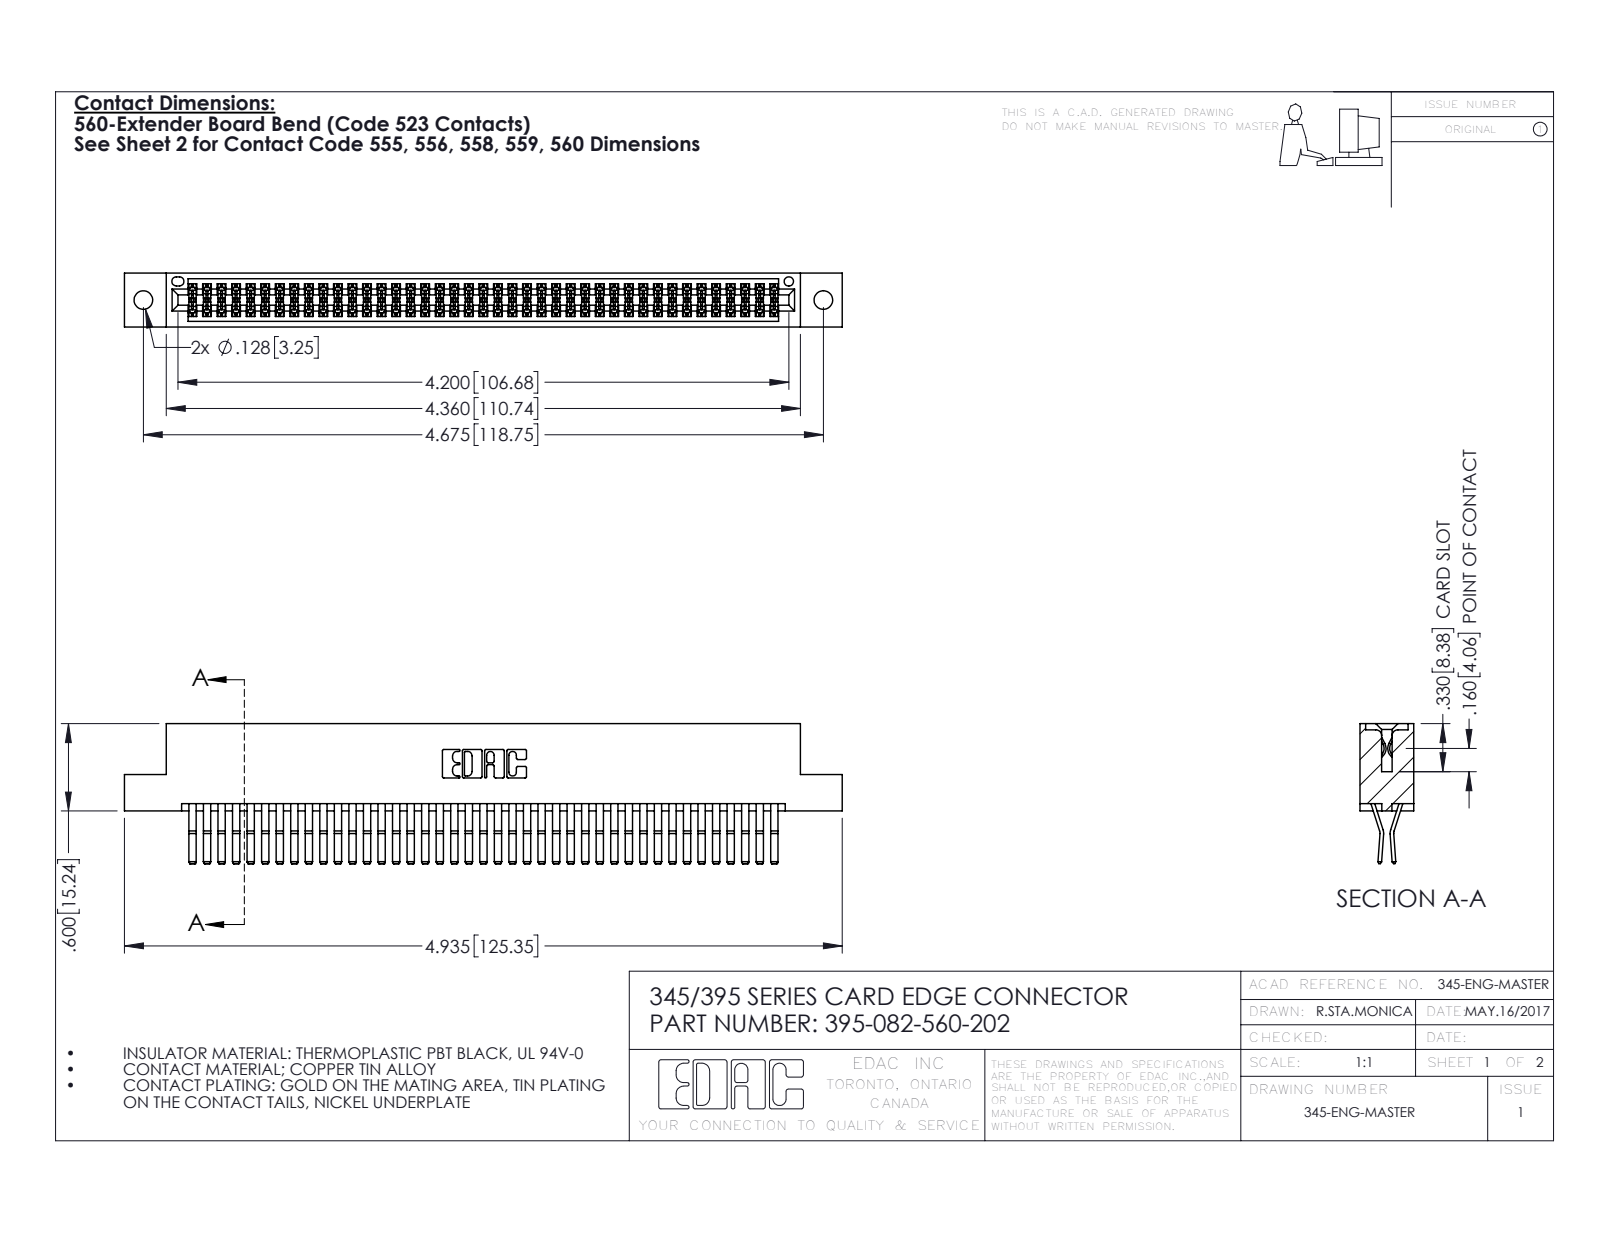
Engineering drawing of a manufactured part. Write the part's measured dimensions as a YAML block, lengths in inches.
part_name: "395-082-560-202; 345-292-001_560 Tail; 345 Part_Flush Mounting Lugs - 0.128 Dia"
step_written_by: "SolidWorks 2016 (CONFIG_CONTROL_DESIGN)"
units: inches
bodies: {solids: 83, faces: 4390, planar: 2786, cylindrical: 1604, other: 0}
overall_size: [4.935, 0.962, 0.37]
volume: 0.773
surface_area: 30.71
round_holes:
  - {diameter: 0.128, count: 2}
  - {diameter: 0.064, count: 1}
partial_cylinders:
  - {radius: 0.006, count: 123}
  - {radius: 0.01, count: 22}
  - {radius: 0.007, count: 6}
  - {radius: 0.031, count: 6}
  - {radius: 0.026, count: 3}
  - {radius: 0.01, count: 2}
  - {radius: 0.014, count: 2}
  - {radius: 0.019, count: 2}
face_to_face_distances: [0.025, 0.298, 0.072, 0.37, 0.2, 0.098, 0.272, 0.225, 0.175, 0.149]
hole_center_spacings: [0.27, 4.439, 4.675]
